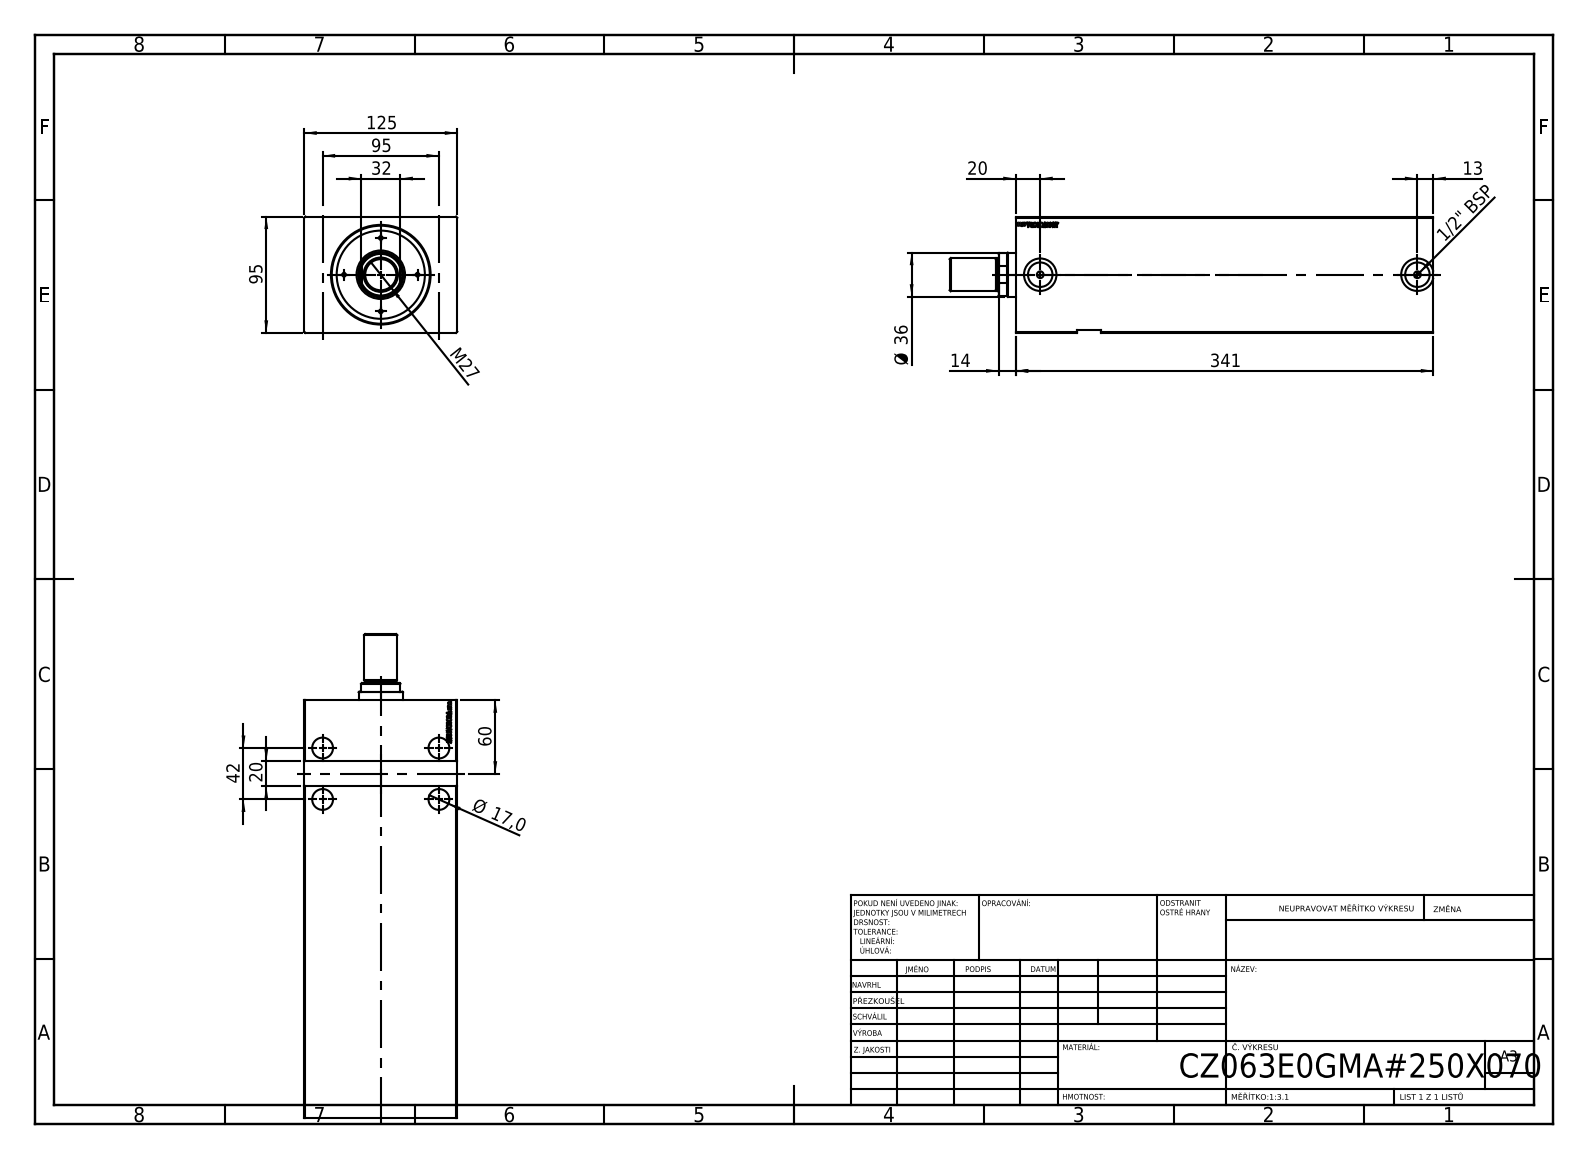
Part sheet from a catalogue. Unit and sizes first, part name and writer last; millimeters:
Units: millimetres
Overall size (bounding box): 341 × 125 × 95
Round holes (diameter × count): ⌀17 ×4, ⌀5.5 ×2, ⌀8 ×2, ⌀20 ×2, ⌀26.5 ×2, ⌀36 ×1, ⌀63 ×1, ⌀80 ×1
Main face-to-face distances: 95, 125, 341, 320.2, 20.8, 2, 93, 14, 306.2, 327
Hole centre spacings: 42, 95, 103.87, 27.02, 49.09, 68.01, 79.4, 231.58
Volume: 2 924 000 mm³ · Surface area: 258 070 mm²
Bodies: 1 solid, 804 faces (393 planar, 29 cylindrical, 382 other)
STEP written by: SolidWorks 2019 (CONFIG_CONTROL_DESIGN)
